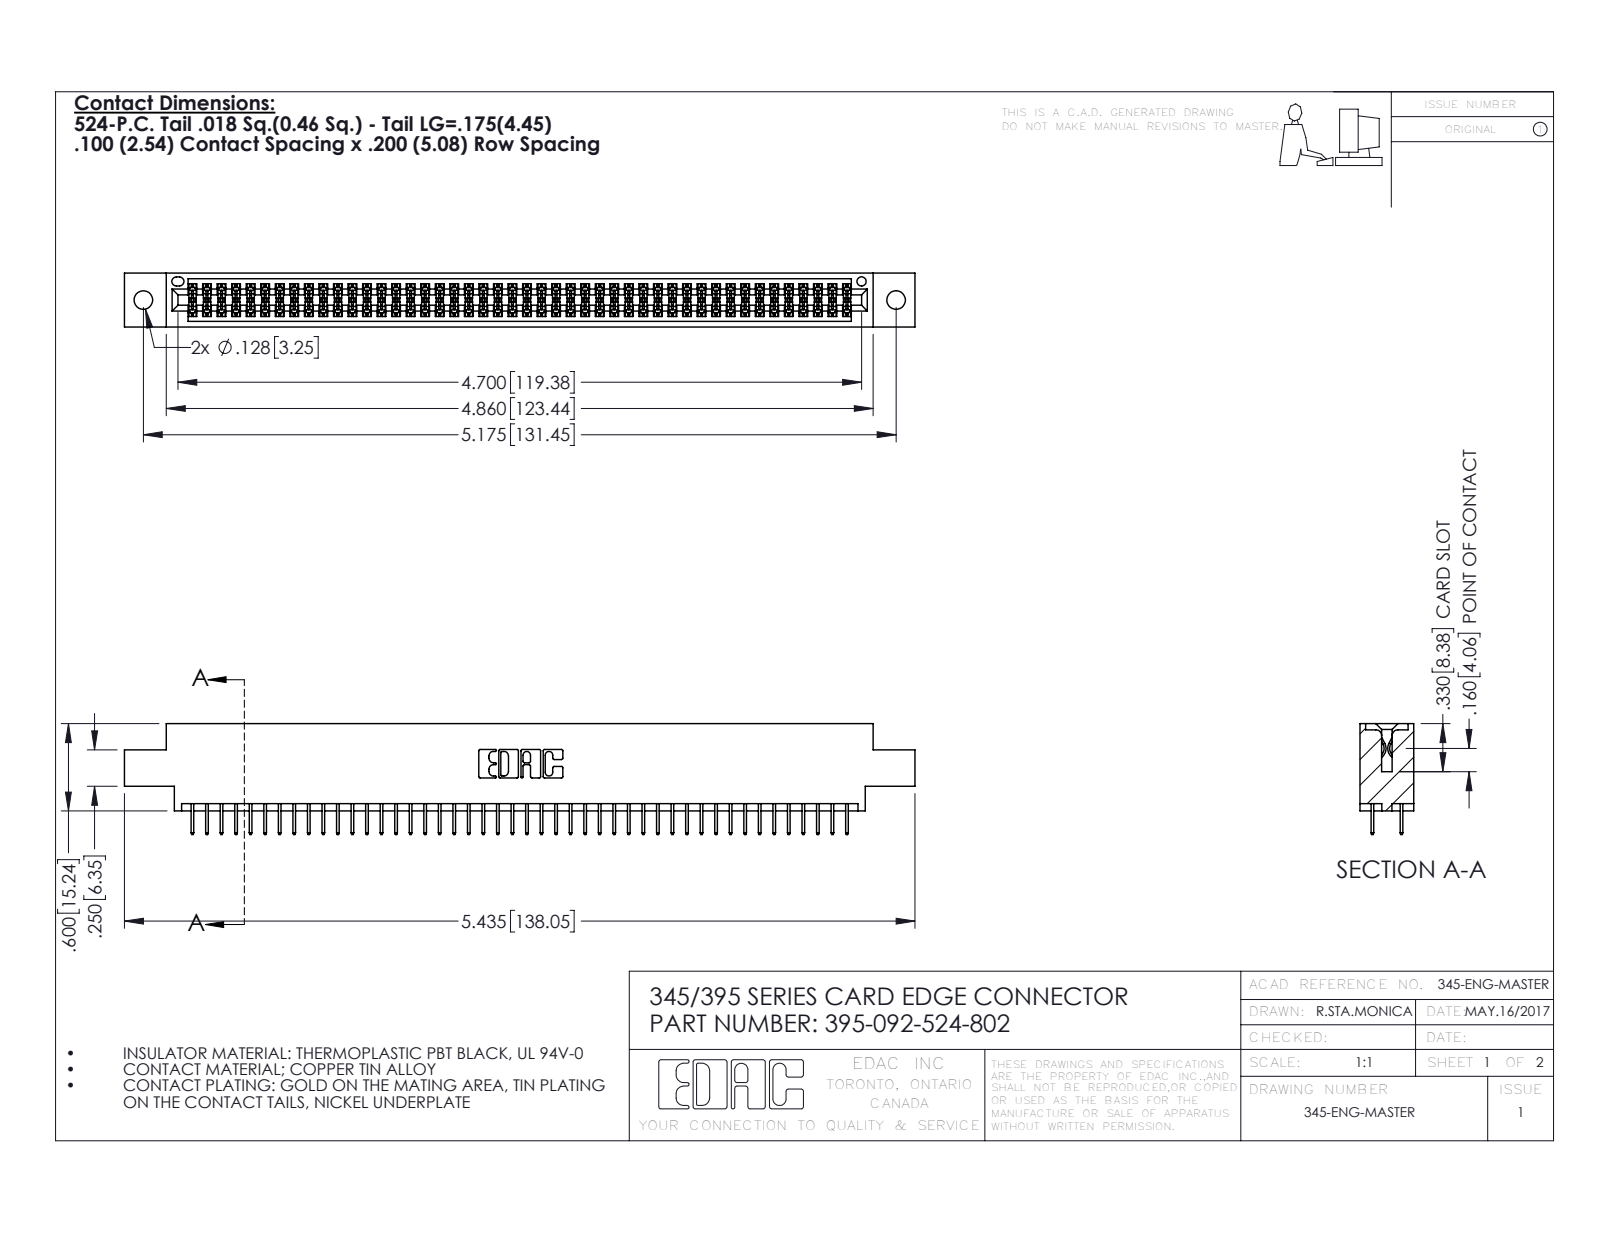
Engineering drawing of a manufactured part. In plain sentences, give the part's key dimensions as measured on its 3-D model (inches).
The part is named "345 Part_0.170 Offset - 0.128 Dia; 345-292-001_345-293-124; 395-092-524-802". Its 3-D file was written by "SolidWorks 2016 (CONFIG_CONTROL_DESIGN)". It is 93 solids with 5098 faces: 3672 planar, 1426 cylindrical and 0 other. Overall it measures 5.435 by 0.762 by 0.37 inches. Its volume is 0.803 cubic inches and its surface area 29.5 square inches. Round holes: 2 of diameter 0.128, 1 of diameter 0.064. Partial cylindrical surfaces (rounded edges, fillets, slot ends): 138 of radius 0.006, 22 of radius 0.01, 6 of radius 0.007, 6 of radius 0.031, 3 of radius 0.026, 2 of radius 0.014, 2 of radius 0.019, 2 of radius 0.022. The main face-to-face distances are 0.072, 0.298, 0.37, 0.2, 0.098, 0.272, 0.025, 0.225, 0.175, 0.072. The hole center spacings are 0.27, 4.939, 5.175.
